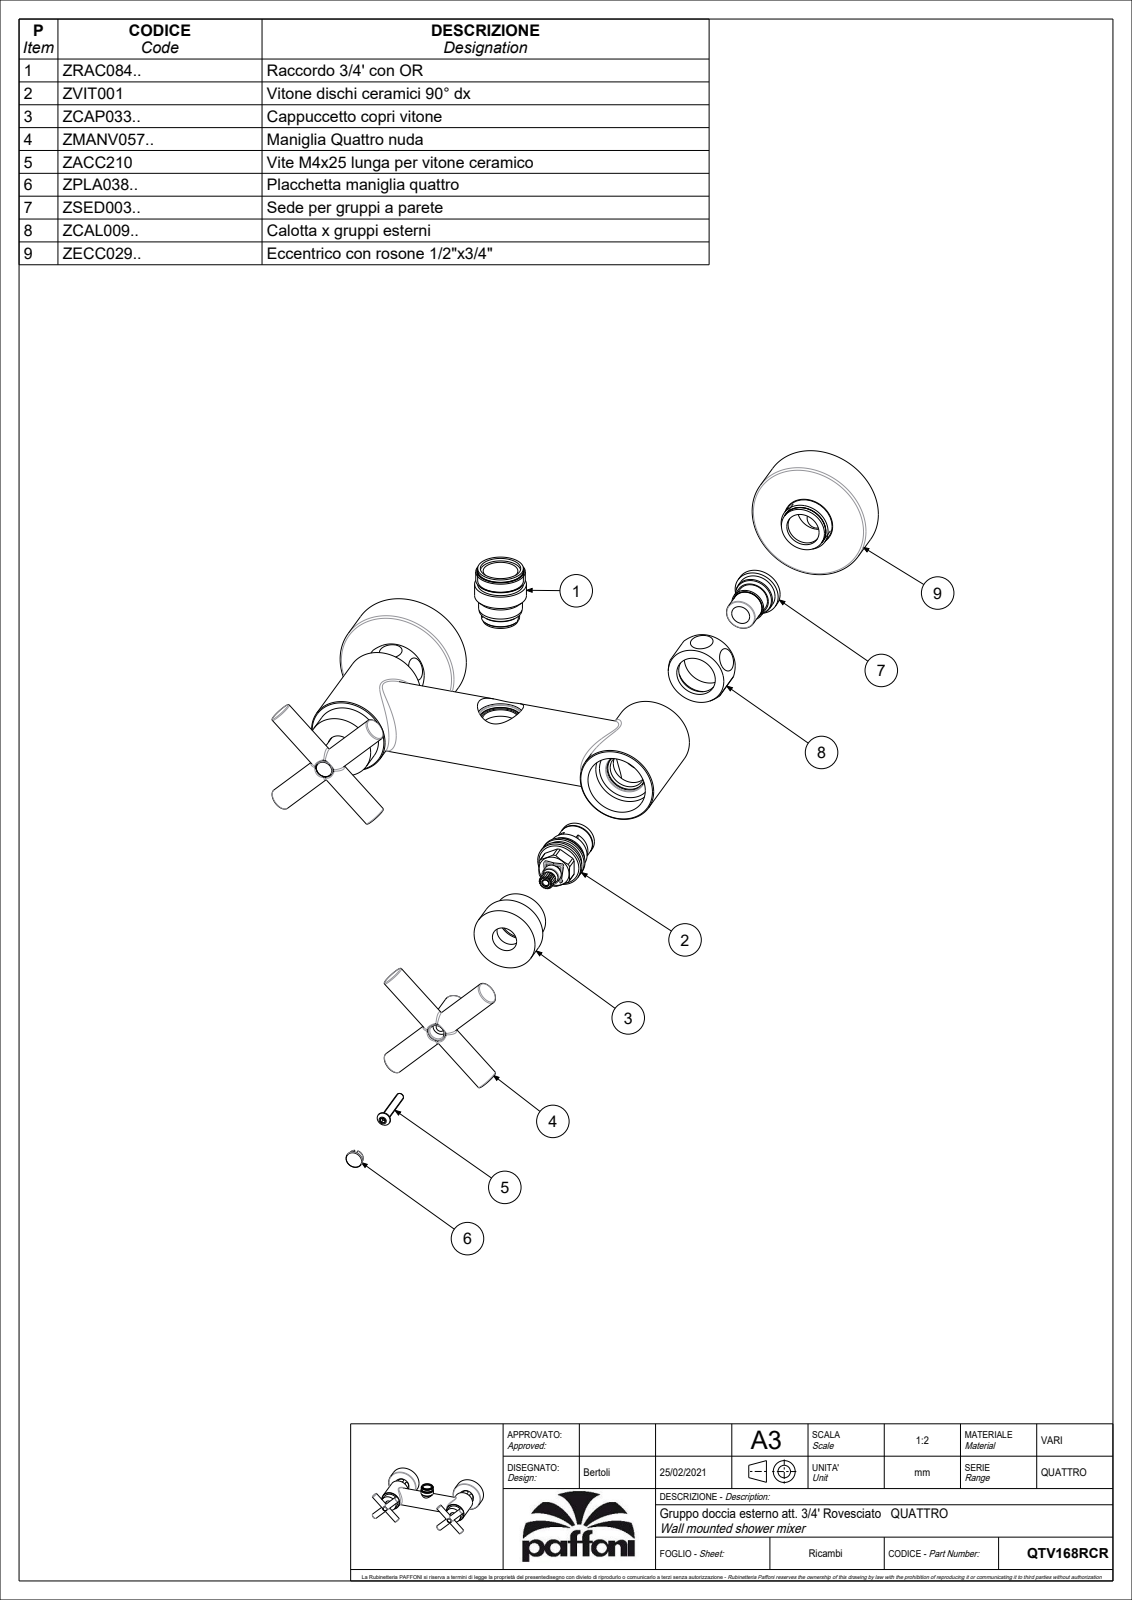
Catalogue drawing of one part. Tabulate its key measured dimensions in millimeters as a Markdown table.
| quantity | value |
| --- | --- |
| part name | QTV168RCR |
| STEP written by | CREO PARAMETRIC BY PTC INC, 2020044 (CONFIG_CONTROL_DESIGN) |
| units | millimeters |
| bodies | 3 solids, 923 faces (451 planar, 254 cylindrical, 218 other) |
| overall size | 213.5 × 132 × 68.25 |
| volume | 231 814 mm³ |
| surface area | 118 776 mm² |
| round holes (diameter × count) | 3.3 × 2, 4.5 × 2, 7 × 2, 8 × 2, 8.8 × 2, 9.5 × 2, 10 × 2, 13.5 × 2, 16.3 × 2, 16.7 × 2, 18 × 2, 21.5 × 2 |
| round bosses / shafts (diameter × count) | 12 × 4, 24 × 3, 63.5 × 2, 41 × 2, 27 × 2, 20.5 × 2, 18.6 × 2, 17.6 × 2 |
| partial cylindrical surfaces (radius × count) | 0.1 × 34, 0.5 × 4, 1 × 4, 3 × 2, 9.4 × 2 |
| main face-to-face distances | 0.6, 67.8, 10, 19.1, 18.5, 28.5, 57.8, 11, 86.9, 86.3 |
| hole center spacings | 150 |
